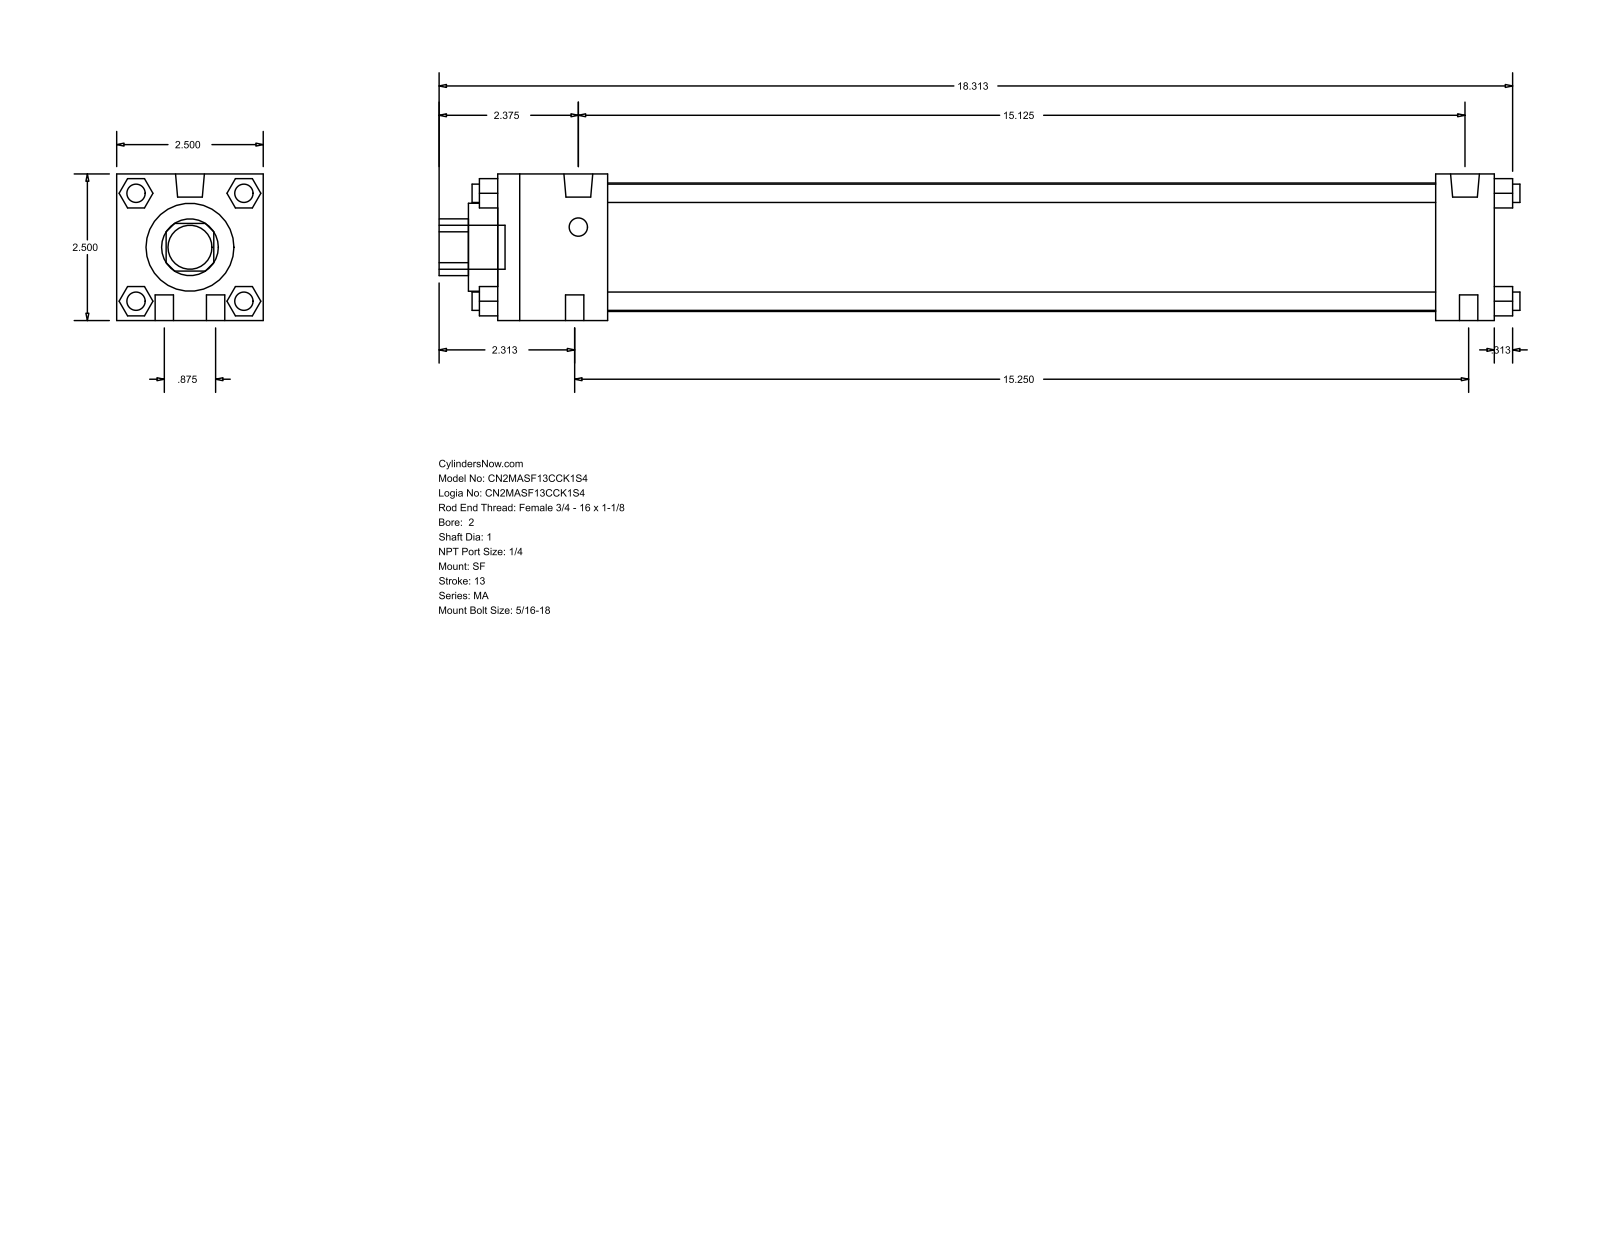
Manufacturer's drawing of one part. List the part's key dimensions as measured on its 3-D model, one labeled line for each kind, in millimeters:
Part name (STEP PRODUCT): MA_SF__0200_1
STEP written by: GSSL Pune (CONFIG_CONTROL_DESIGN)
Units: millimetres
Bodies: 0 solids, 124 faces (94 planar, 30 cylindrical, 0 other)
Overall size (bounding box): 468.31 × 63.5 × 63.5
Round holes (diameter × count): ⌀25.4 ×1, ⌀38.1 ×1, ⌀55.63 ×1
Round bosses / shafts (diameter × count): ⌀7.94 ×10, ⌀12.49 ×2, ⌀19.05 ×1
Partial cylindrical surfaces — rounded edges, fillets, slot ends (radius × count): R12.29 ×1
Main face-to-face distances: 63.5, 431.8, 12.7, 25.4, 406.4, 47.63, 358.77, 384.17, 40.47, 23.37
